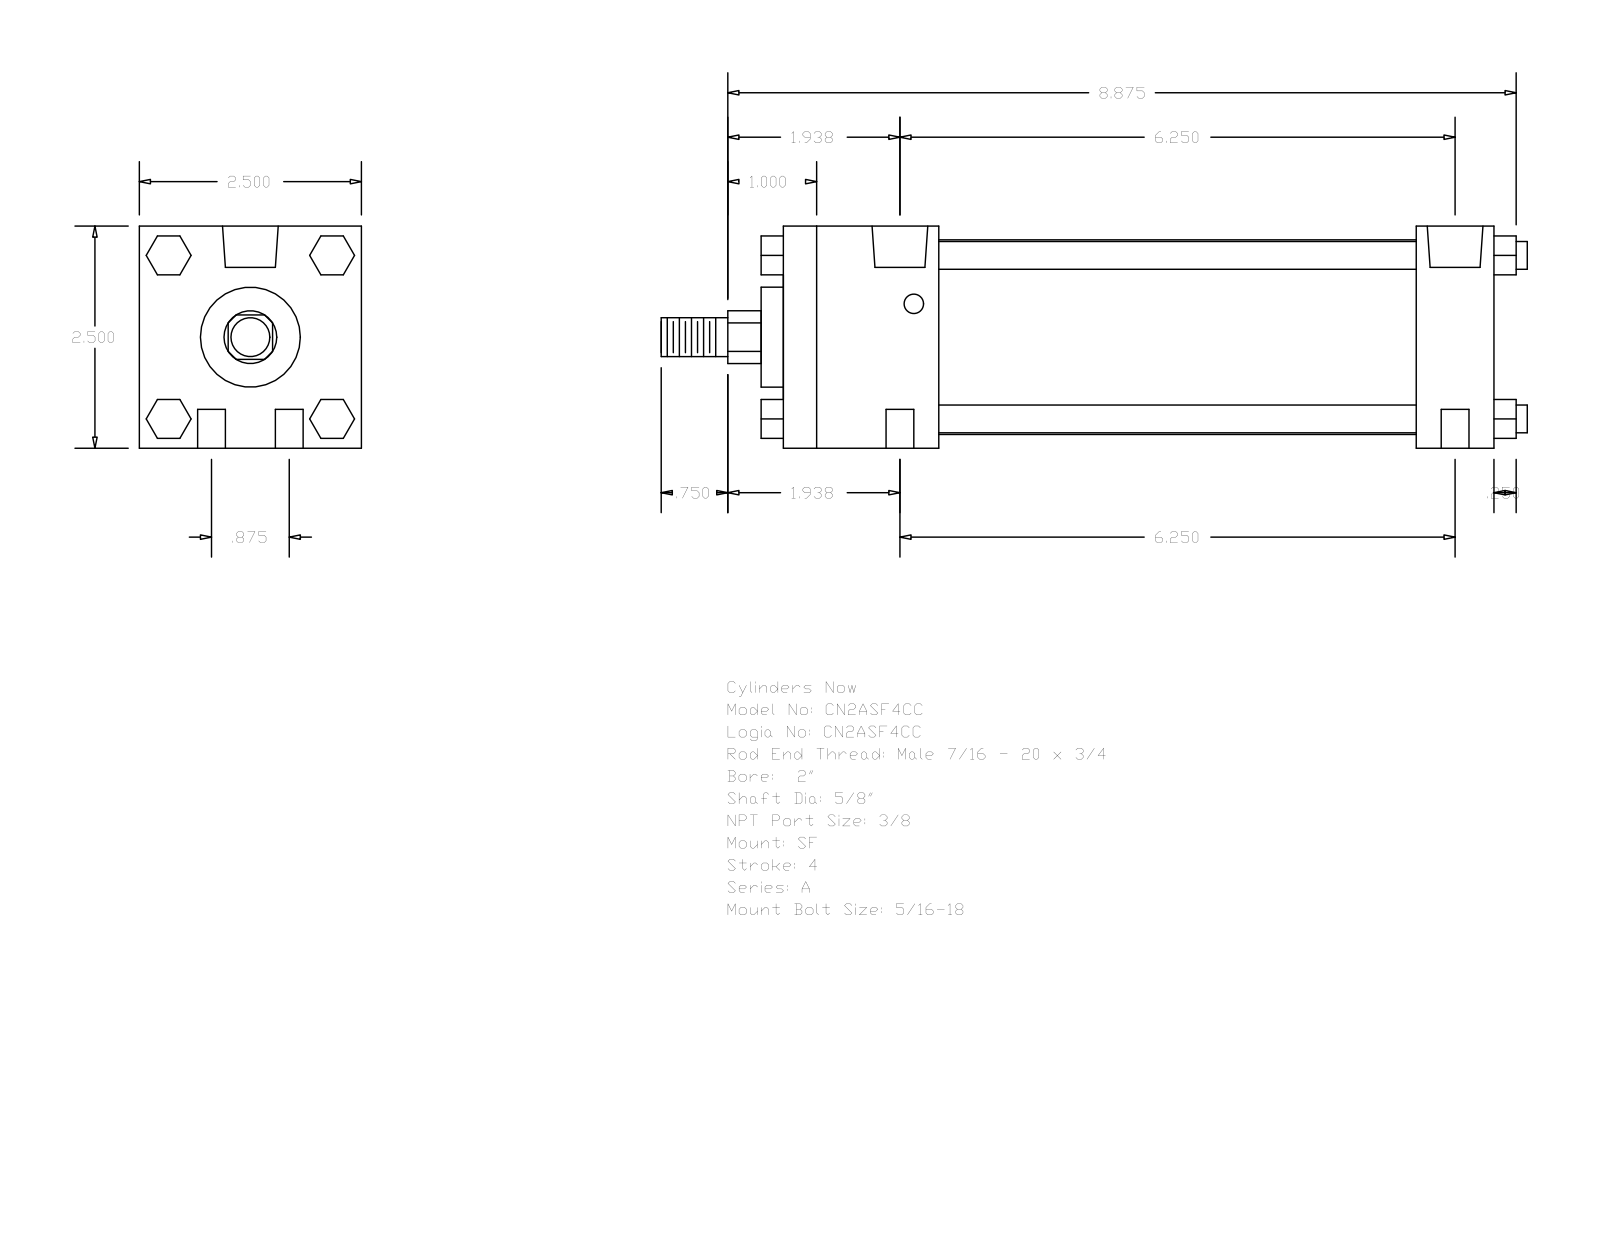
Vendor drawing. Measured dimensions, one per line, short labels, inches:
name: A_SF__0200_0.625
written by: GSSL Pune (CONFIG_CONTROL_DESIGN)
unit: in
bodies: 0 solids, 124 faces (94 planar, 30 cylindrical, 0 other)
size: 9.75 × 2.5 × 2.5
holes: 4× ⌀0.313, 2× ⌀0.219, 2× ⌀0.627
bosses: 4× ⌀0.313, 1× ⌀2.19, 1× ⌀1.125, 1× ⌀0.625, 1× ⌀0.437
rounds: 1× R0.297
face distances: 2.5, 8, 7.125, 0.875, 1.75, 5.375, 6.25, 2, 0.25, 7.375
hole spacings: 0.437, 6.265, 6.25, 0.875, 6.311, 5.937
